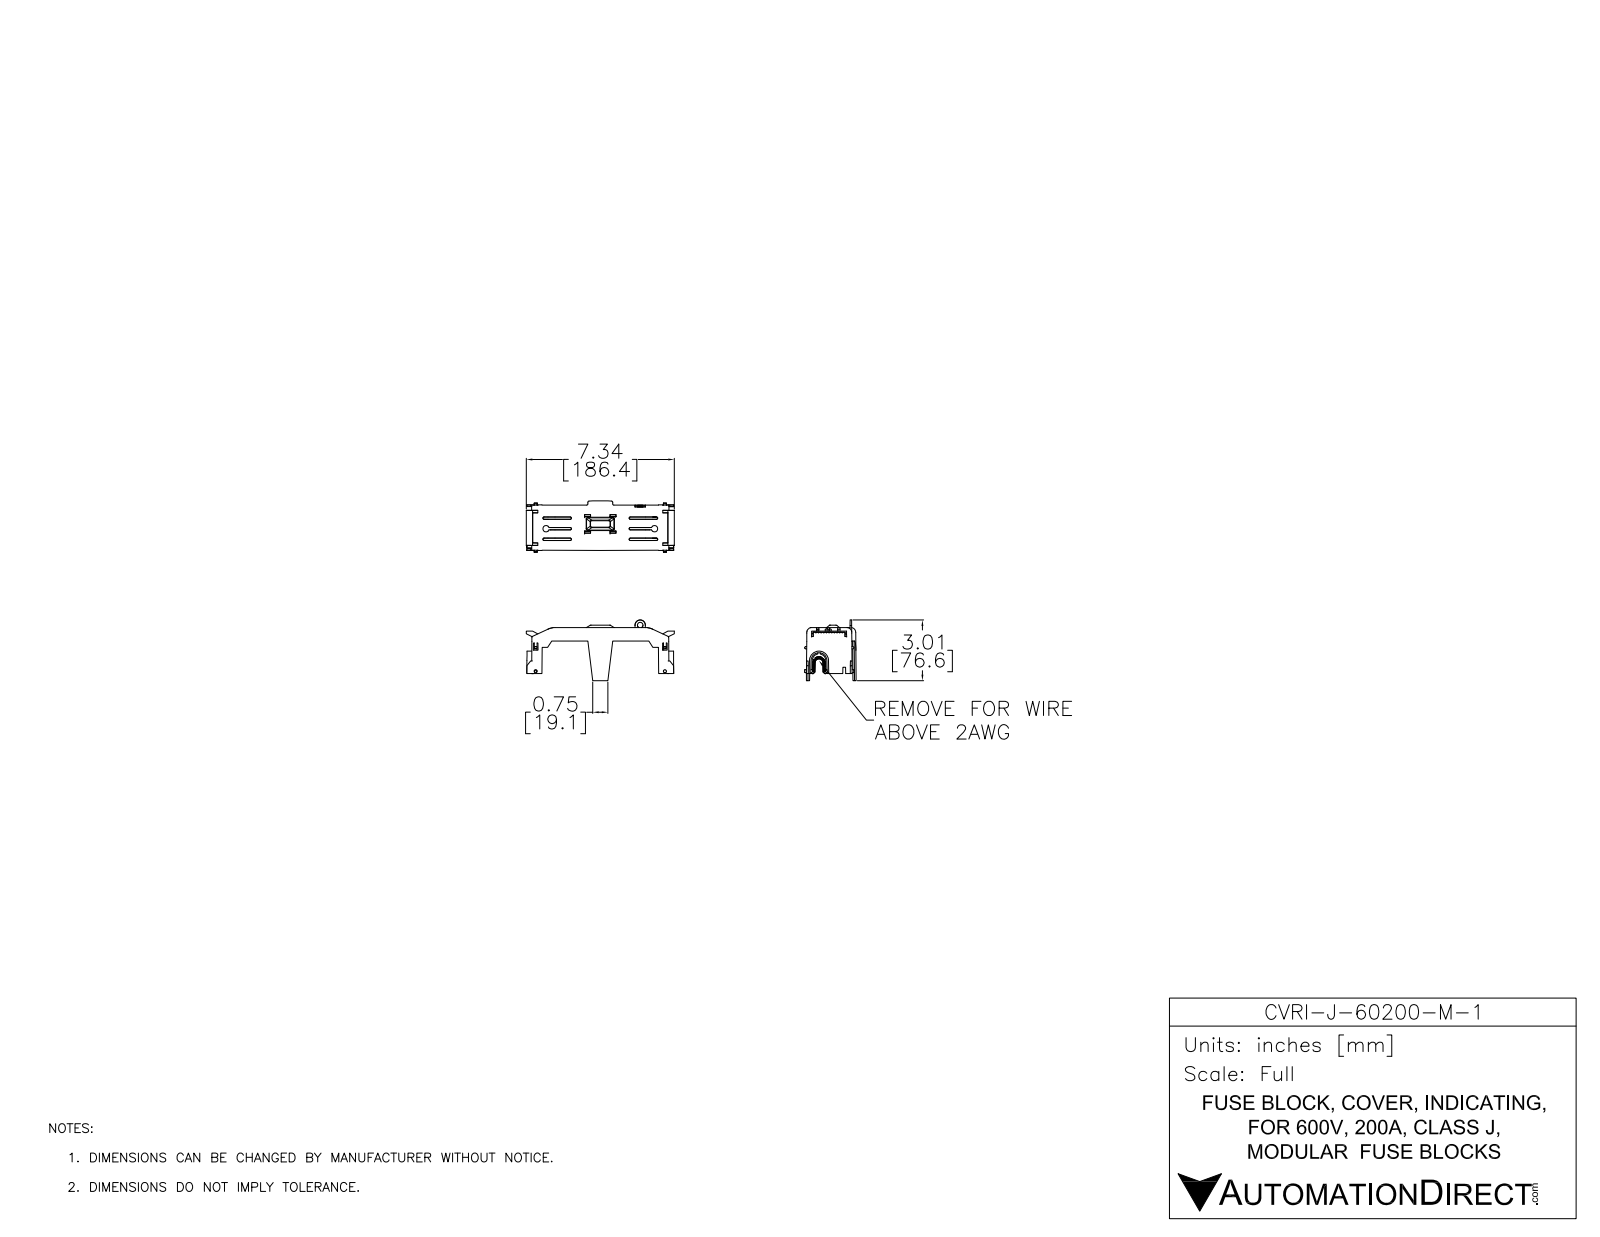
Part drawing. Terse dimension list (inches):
name: CVRI-J-60200-M-1
written by: SolidWorks 2017 (AUTOMOTIVE_DESIGN)
unit: in
bodies: 1 solid, 1408 faces (920 planar, 113 cylindrical, 375 other)
size: 7.34 × 3.014 × 2.553
volume: 3.494 in³; area: 95.88 in²
holes: 1× ⌀0.276
rounds: 12× R0.039, 9× R0.236, 8× R0.118, 7× R0.157, 6× R0.035, 4× R0.059, 2× R0.01, 2× R0.02
face distances: 0.079, 0.197, 0.118, 0.276, 0.512, 0.606, 0.095, 0.174, 0.803, 0.256
